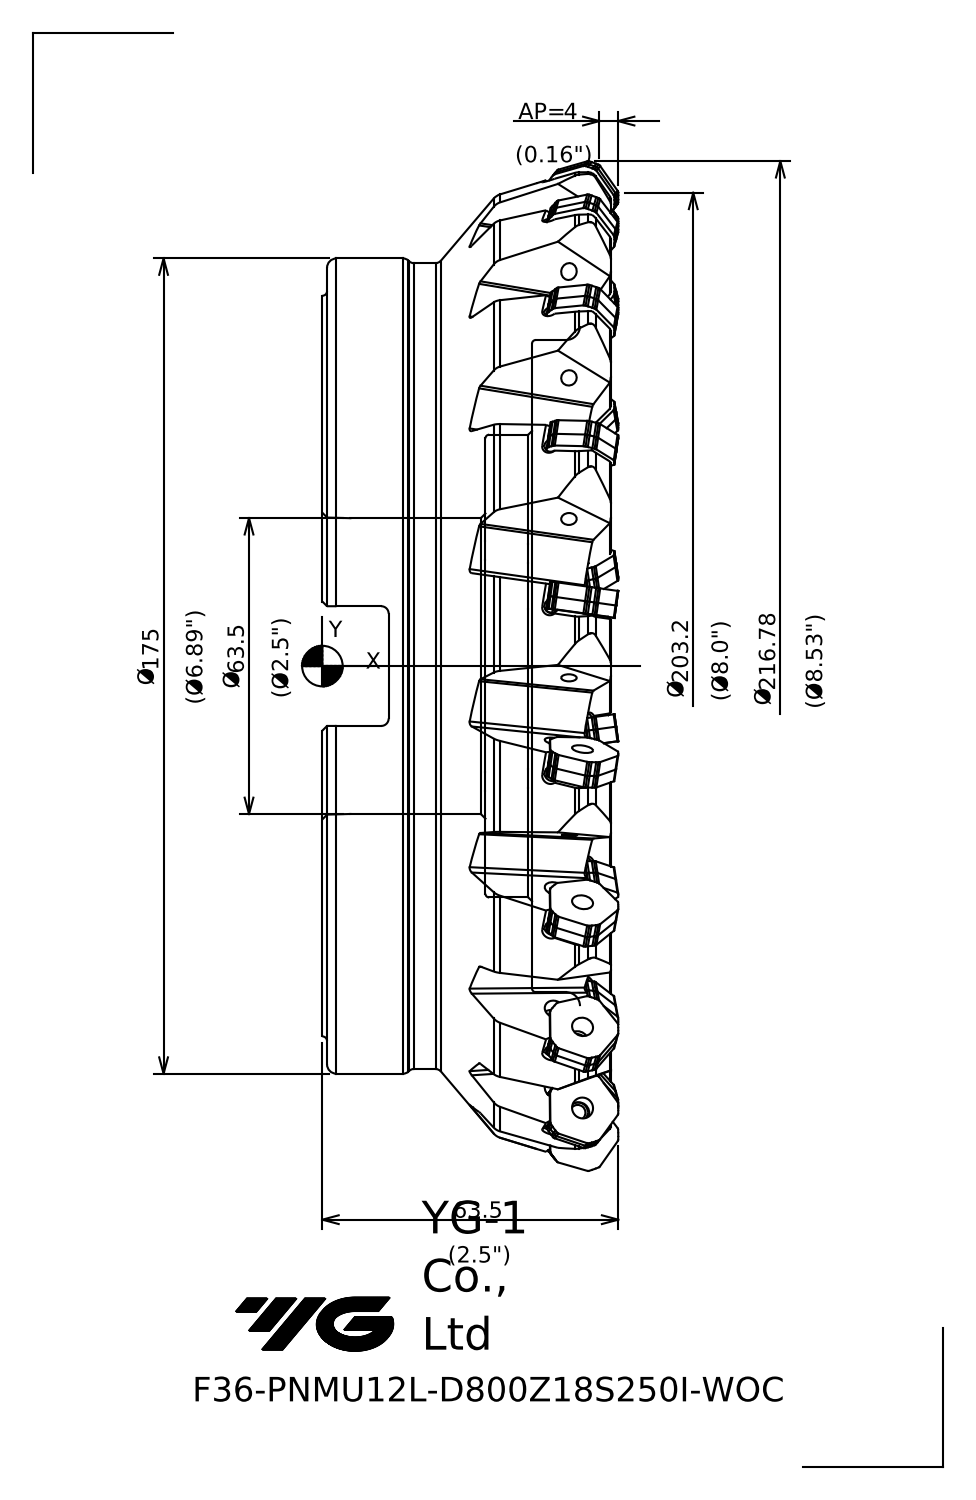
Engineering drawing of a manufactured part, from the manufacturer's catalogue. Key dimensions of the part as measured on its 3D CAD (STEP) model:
Part name (STEP PRODUCT): 10221A6C8B27vrof
STEP written by: SIEMENS PLM Software NX 10.0 (AP203_CONFIGURATION_CONTROLLED_3D_DESIGN_OF_MECHANICAL_PARTS_AND_ASSEMBLIES_MIM_LF)
Units: millimetres
Bodies: 1 solid, 167 faces (33 planar, 37 cylindrical, 97 other)
Overall size (bounding box): 216.77 × 216.77 × 63.51
Volume: 1 151 000 mm³ · Surface area: 145 266 mm²
Round holes (diameter × count): ⌀18 ×4, ⌀63.5 ×1, ⌀140 ×1
Round bosses / shafts (diameter × count): ⌀212.6 ×1, ⌀175 ×1, ⌀173 ×1
Partial cylindrical surfaces — rounded edges, fillets, slot ends (radius × count): R10 ×8, R0.8 ×4, R13.75 ×4, R1.6 ×2, R41 ×1
Main face-to-face distances: 45, 10, 35, 30.78, 20.78, 14.22, 44, 34, 13.22, 1
Hole centre spacings: 50.8, 71.84, 101.6
